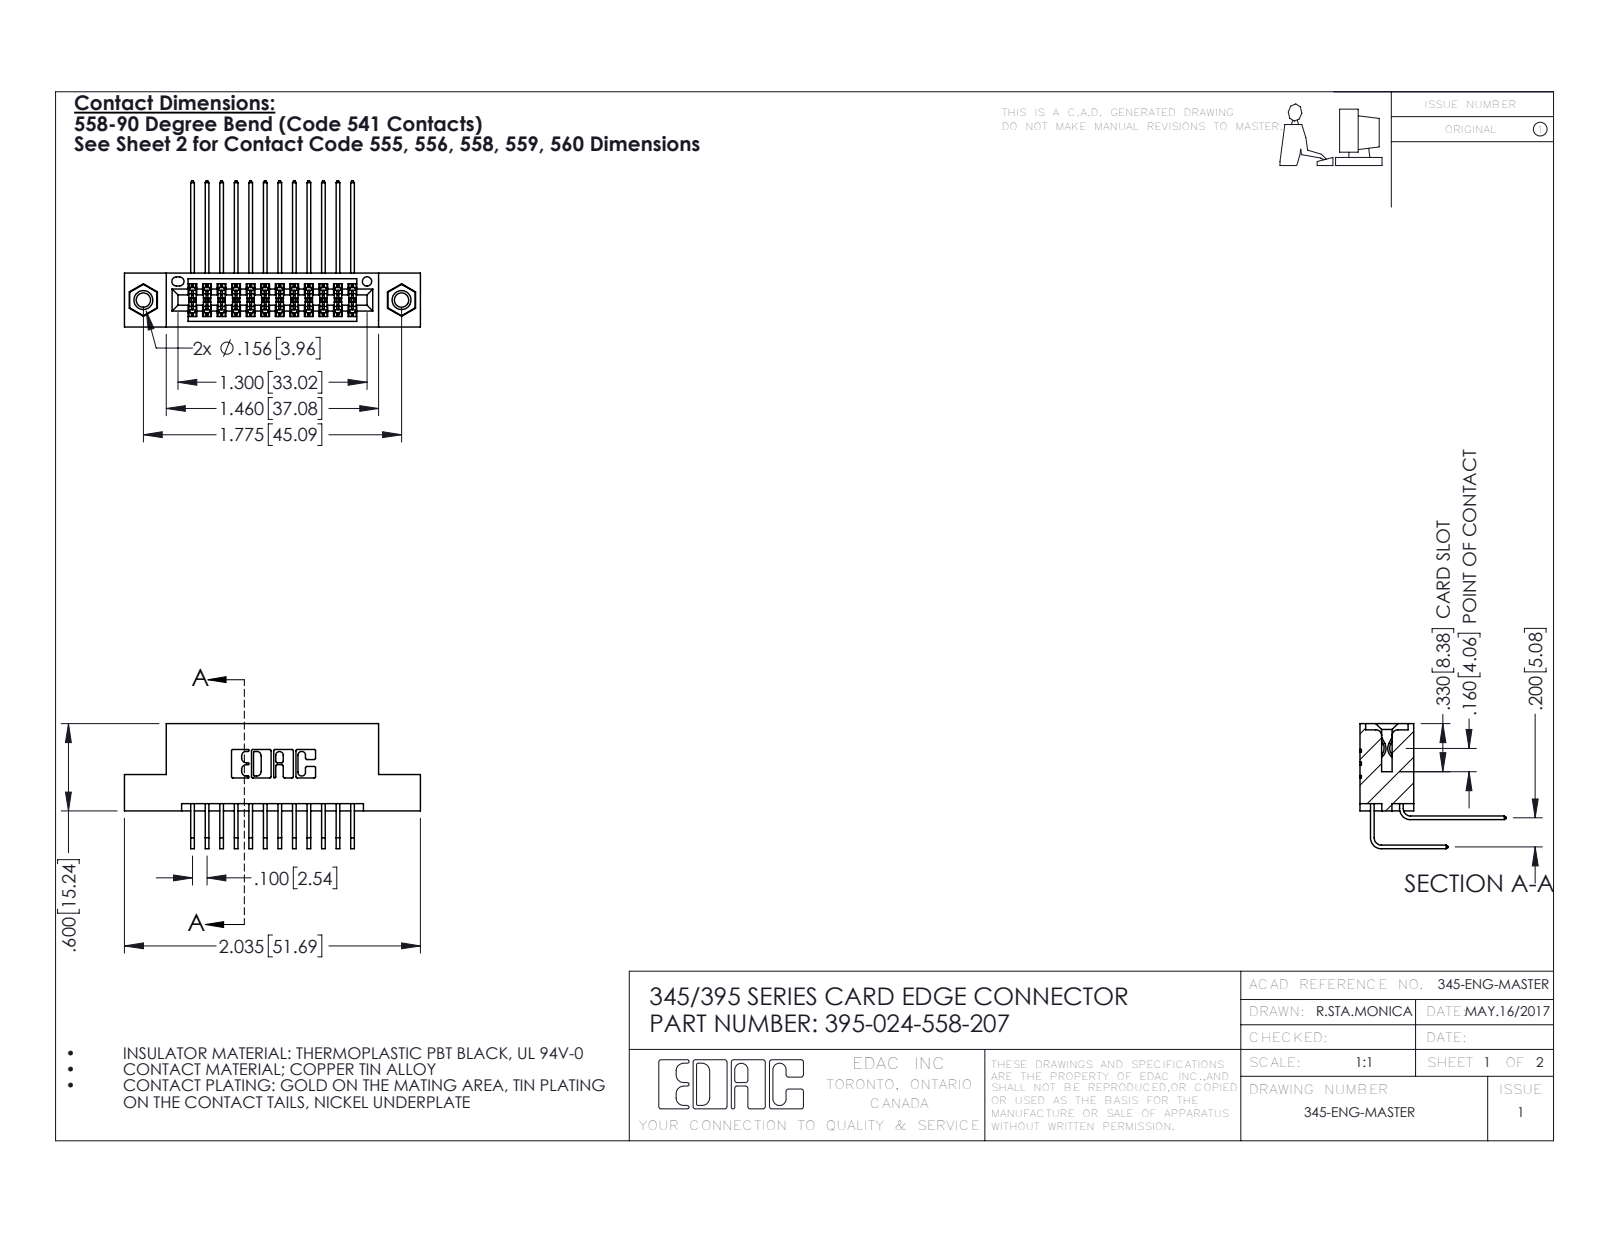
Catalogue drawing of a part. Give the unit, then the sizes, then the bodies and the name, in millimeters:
Units: millimetres
Overall size (bounding box): 51.7 × 25.5 × 21.8
Round holes (diameter × count): ⌀2.5 ×2, ⌀3.2 ×2, ⌀4 ×2, ⌀1.6 ×1
Round bosses / shafts (diameter × count): ⌀3.9 ×2
Partial cylindrical surfaces — rounded edges, fillets, slot ends (radius × count): R0.2 ×37, R0.3 ×22, R0.2 ×6, R0.8 ×6, R0.7 ×3, R0.4 ×2, R0.5 ×2, R0.6 ×2
Main face-to-face distances: 5.1, 1.8, 7.6, 9.4, 2.5, 6.9, 0.6, 5.7, 2.5, 7.2
Hole centre spacings: 6.9, 39.2, 45.1
Volume: 4 870 mm³ · Surface area: 7 290 mm²
Bodies: 27 solids, 1434 faces (952 planar, 466 cylindrical, 16 other)
Part name (STEP PRODUCT): 345 Part_Flush Mounting Lugs - 0.156 Dia-TI; 345-292-001_558 559 Tail - 1; 345-250-001_345-250-005-103; 345-292-001_558 Tail - 2 (+1 more)
STEP written by: SolidWorks 2016 (CONFIG_CONTROL_DESIGN)
